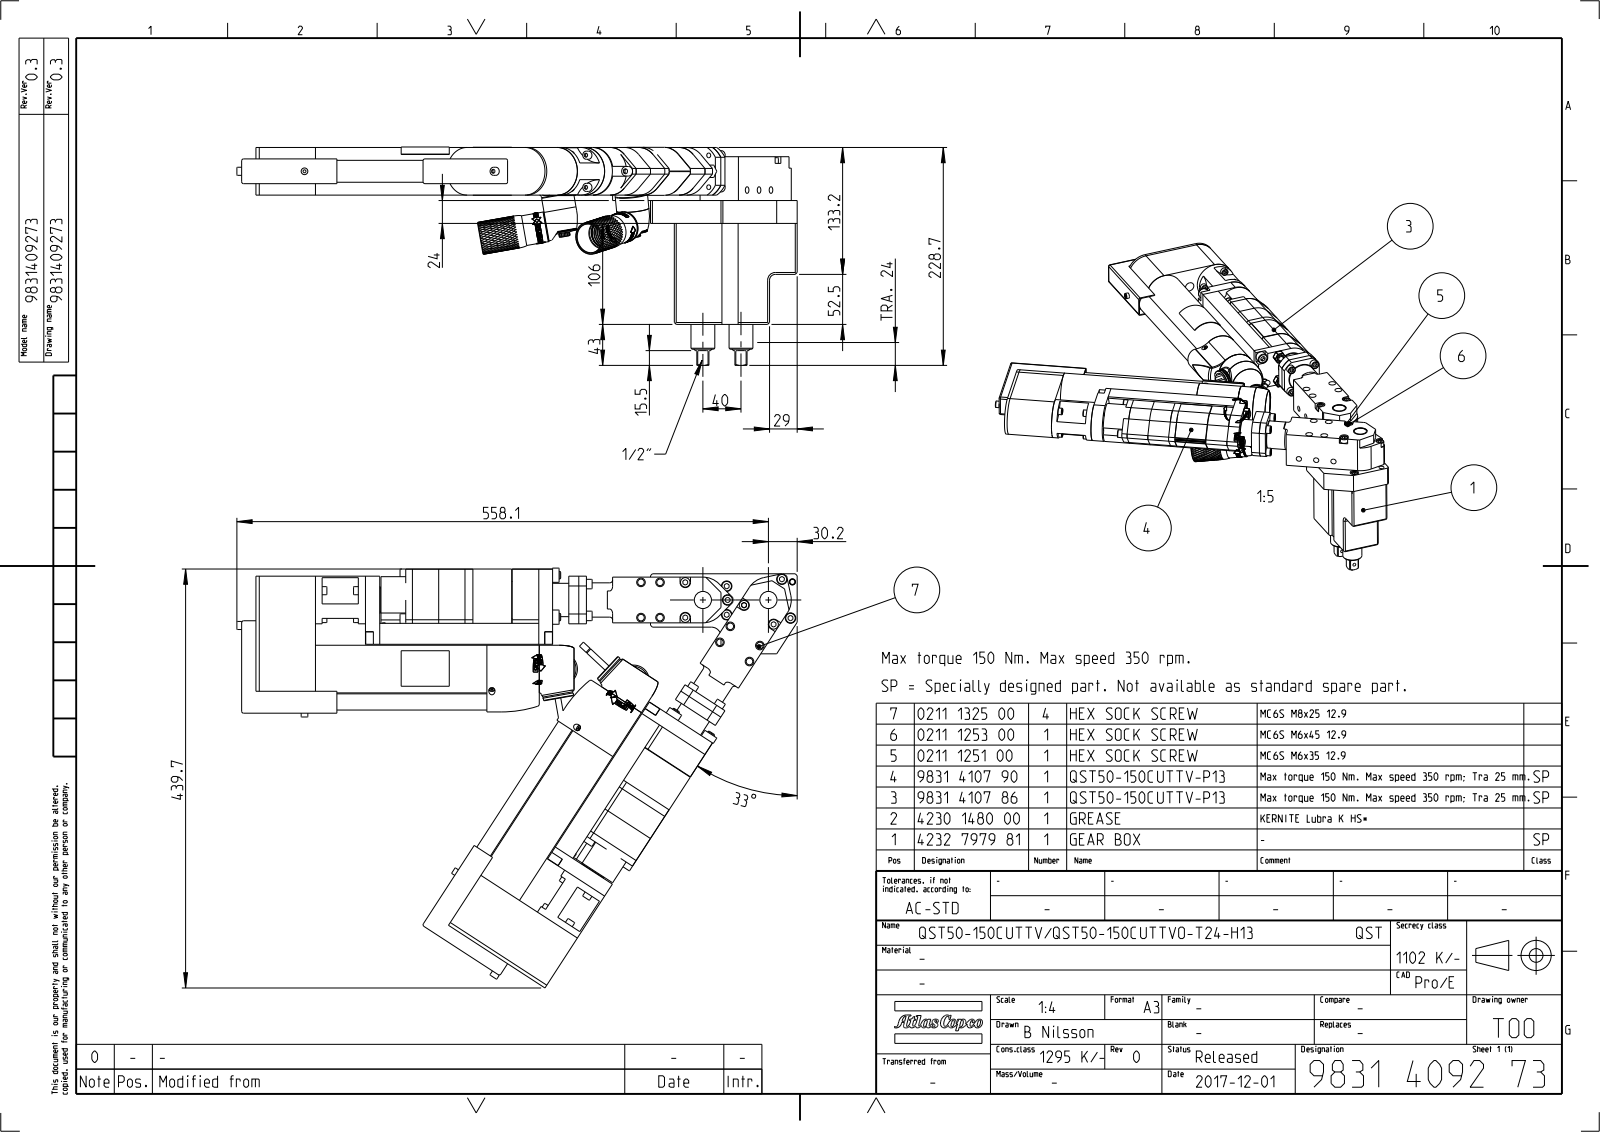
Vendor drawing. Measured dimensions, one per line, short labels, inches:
name: 4232798000; 4090030300; 4232798300; 4232798201 (+8 more)
written by: CREO PARAMETRIC BY PTC INC, 2018100 (CONFIG_CONTROL_DESIGN)
unit: in
bodies: 60 solids, 7421 faces (2460 planar, 2832 cylindrical, 2129 other)
size: 23.161 × 17.311 × 9.013
volume: 176.1 in³; area: 1 739 in²
holes: 37× ⌀0.154, 26× ⌀0.248, 18× ⌀0.315, 16× ⌀0.194, 16× ⌀0.354, 15× ⌀0.13, 14× ⌀0.272, 12× ⌀0.197, 12× ⌀0.217, 12× ⌀0.268, 12× ⌀0.335, 10× ⌀0.177
bosses: 40× ⌀0.197, 25× ⌀0.315, 22× ⌀0.236, 15× ⌀0.157, 6× ⌀1.969, 6× ⌀1.339, 6× ⌀0.118, 6× ⌀0.098
rounds: 70× R0.02, 38× R0.039, 32× R0.079, 16× R0.118, 12× R0.984, 10× R1.28, 8× R0.008, 8× R0.075
face distances: 1.969, 0.039, 0.138, 0.098, 0.472, 0.945, 0.224, 1.398, 2.193, 1.457
hole spacings: 0.768, 1.33, 1.086, 1.483, 0.397, 0.769, 3.306, 2.854
